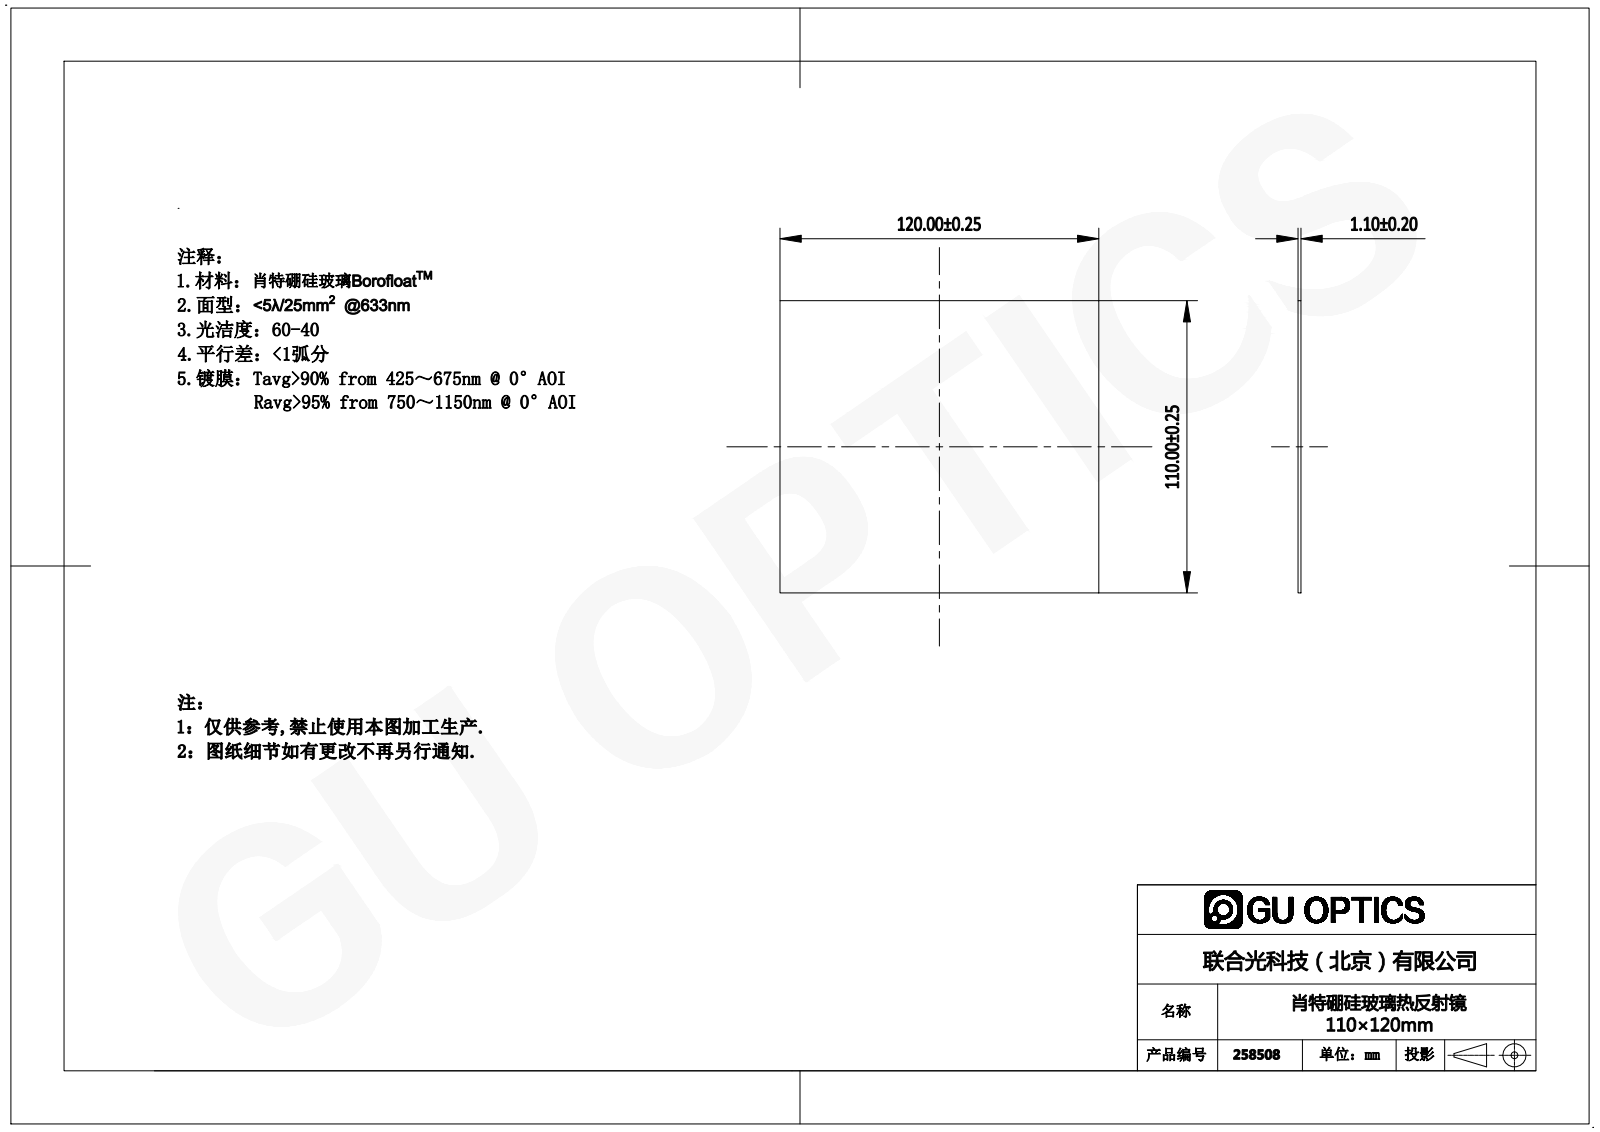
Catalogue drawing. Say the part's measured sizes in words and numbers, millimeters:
The part is named "258508". Its 3-D file was written by "SolidWorks 2016 (AUTOMOTIVE_DESIGN)". It is 1 solid with 6 faces: 6 planar, 0 cylindrical and 0 other. Overall it measures 120 by 110 by 1.1 millimeters. Its volume is 14 520 cubic millimeters and its surface area 26 906 square millimeters. The main face-to-face distances are 1.1, 110, 120.
